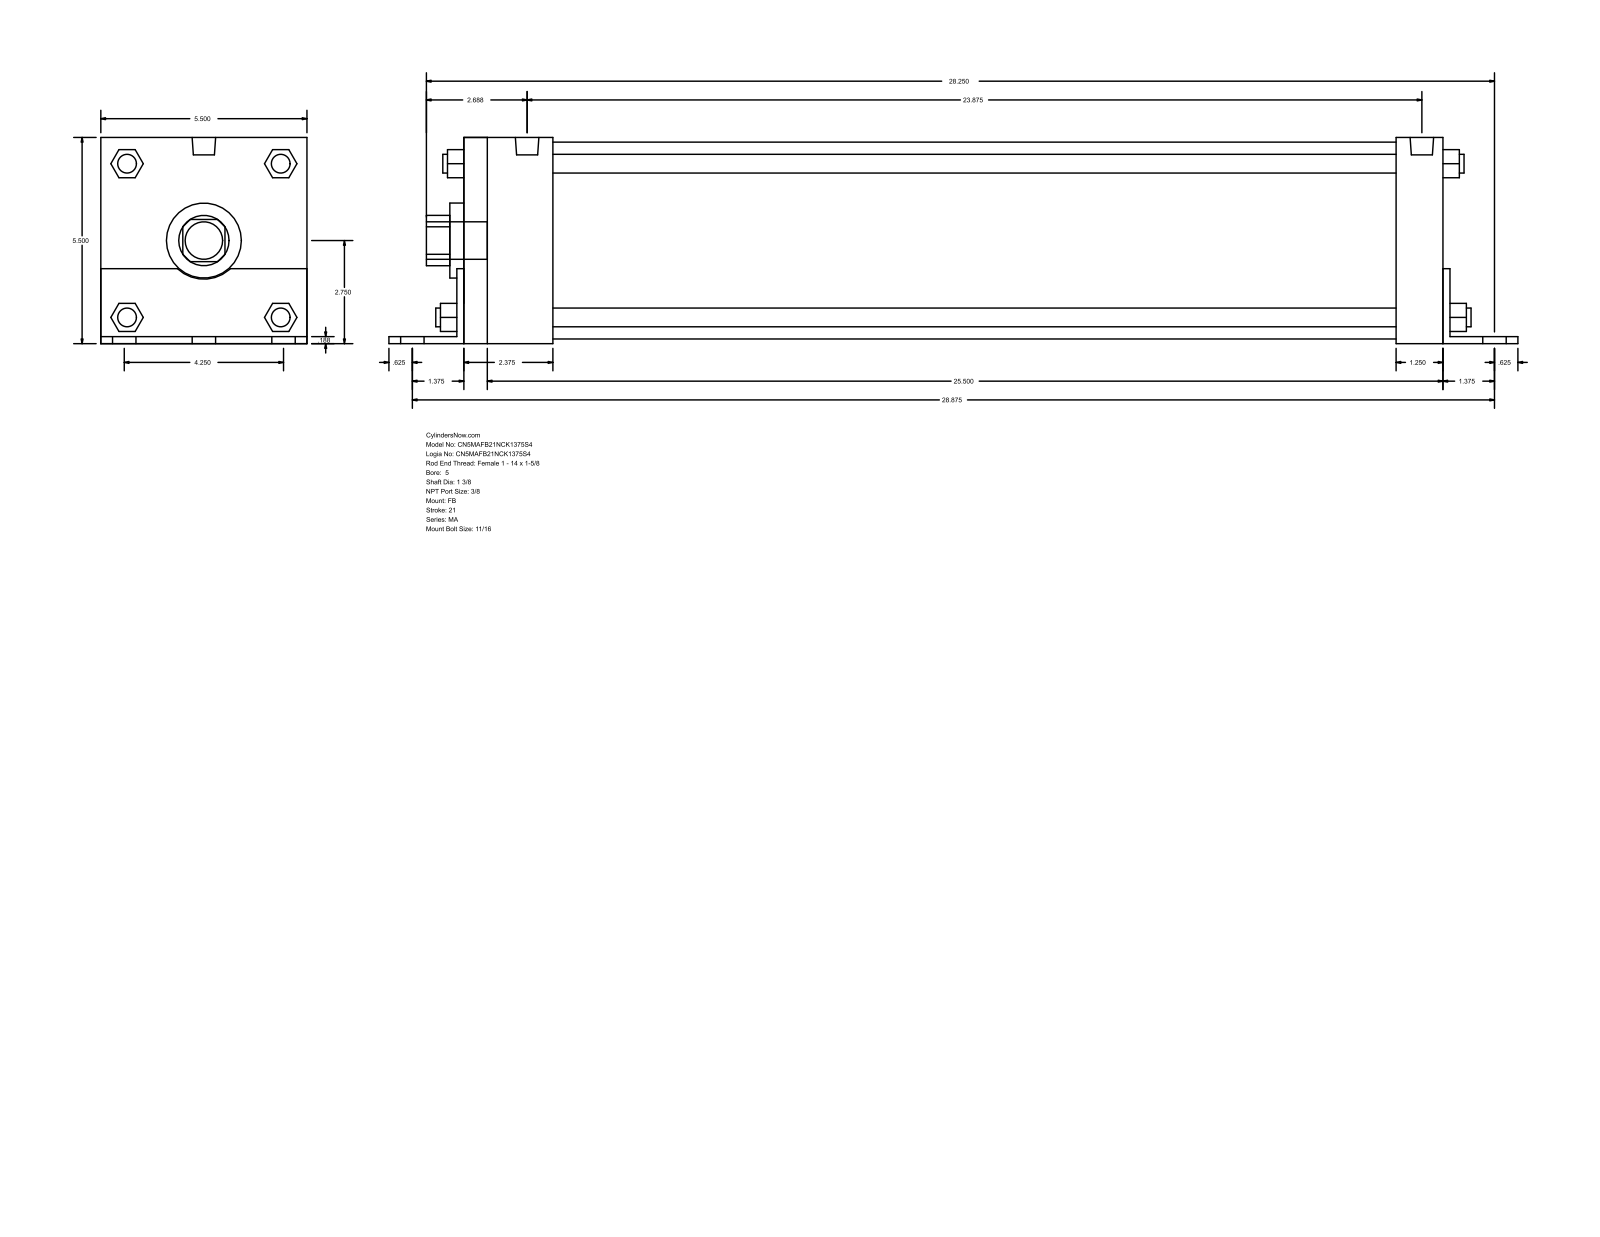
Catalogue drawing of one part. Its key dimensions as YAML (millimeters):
part_name: "MA_FB__0500_1.375"
step_written_by: "GSSL Pune (CONFIG_CONTROL_DESIGN)"
units: millimeters
bodies: {solids: 0, faces: 140, planar: 105, cylindrical: 35, other: 0}
overall_size: [765.17, 139.75, 139.7]
round_holes:
  - {diameter: 34.92, count: 1}
  - {diameter: 50.8, count: 1}
  - {diameter: 133.35, count: 1}
round_bosses_or_shafts:
  - {diameter: 17.46, count: 6}
  - {diameter: 12.7, count: 4}
  - {diameter: 11.11, count: 4}
  - {diameter: 15.93, count: 2}
  - {diameter: 25.4, count: 1}
partial_cylinders:
  - {radius: 17.06, count: 1}
  - {radius: 26.16, count: 1}
face_to_face_distances: [139.7, 4.76, 139.75, 668.34, 4.71, 134.99, 663.58, 673.1, 31.75, 36.51]
